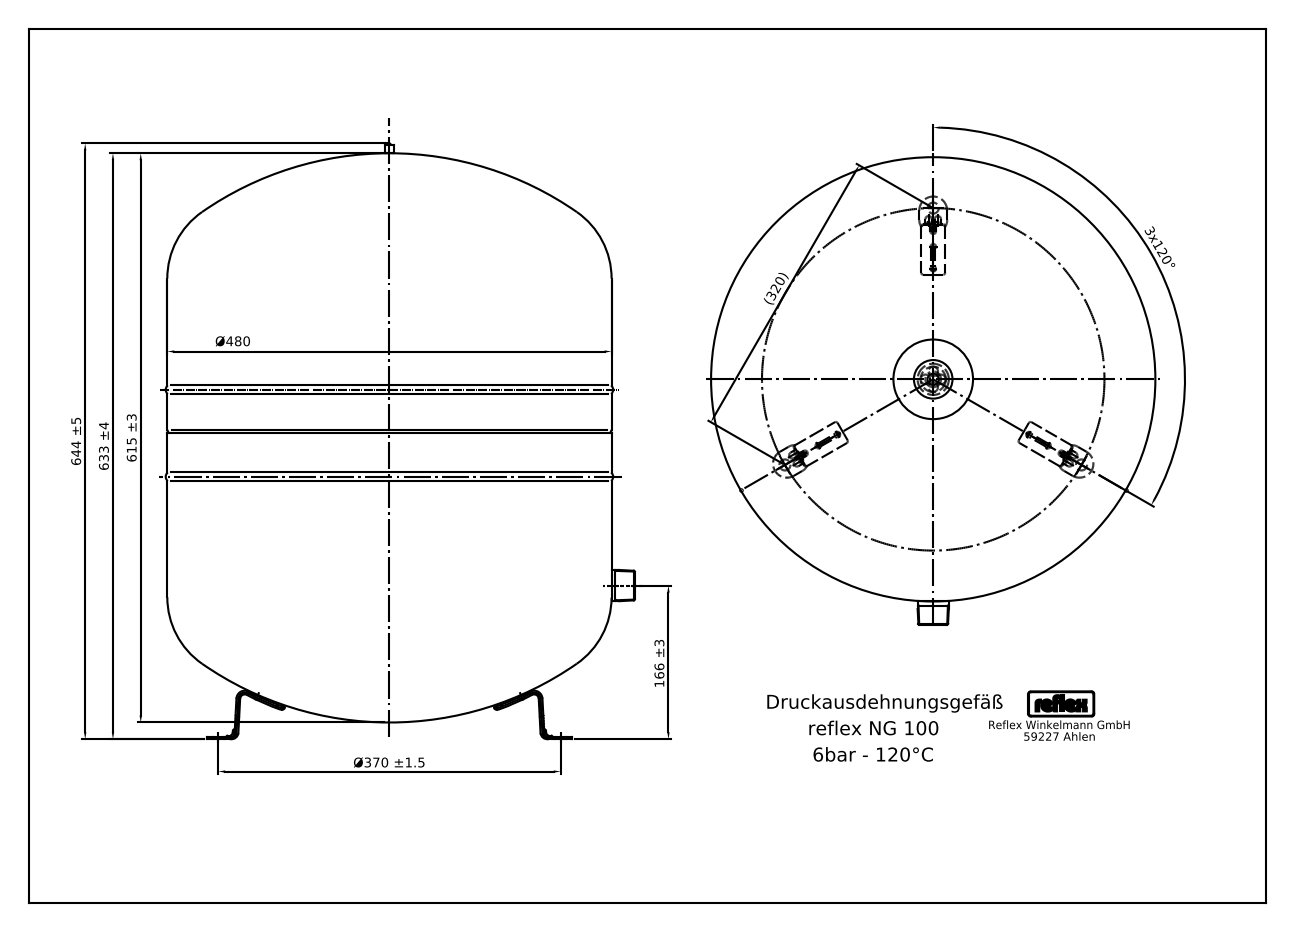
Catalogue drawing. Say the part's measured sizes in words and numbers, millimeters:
Its 3-D file was written by "Mechanical Desktop 2011 (CONFIG_CONTROL_DESIGN)". It is 16 solids with 191 faces: 76 planar, 74 cylindrical and 41 other. Overall it measures 670 by 521 by 512 millimeters. Its volume is 99 680 000 cubic millimeters and its surface area 1 947 000 square millimeters. Round holes: 3 of diameter 15, 1 of diameter 25.7. Round bosses or shafts: 1 of diameter 512, 1 of diameter 480, 1 of diameter 33.7, 1 of diameter 10, 1 of diameter 6. Partial cylindrical surfaces (rounded edges, fillets, slot ends): 9 of radius 148.38, 9 of radius 150.38, 6 of radius 15, 4 of radius 2.81, 3 of radius 1.12, 2 of radius 1.92, 2 of radius 3.38, 2 of radius 4.64. The main face-to-face distances are 380, 179.25, 200.75, 21.5, 328.25, 149, 349.75, 529, 2, 147. The hole center spacings are 320.43, 320.42.
